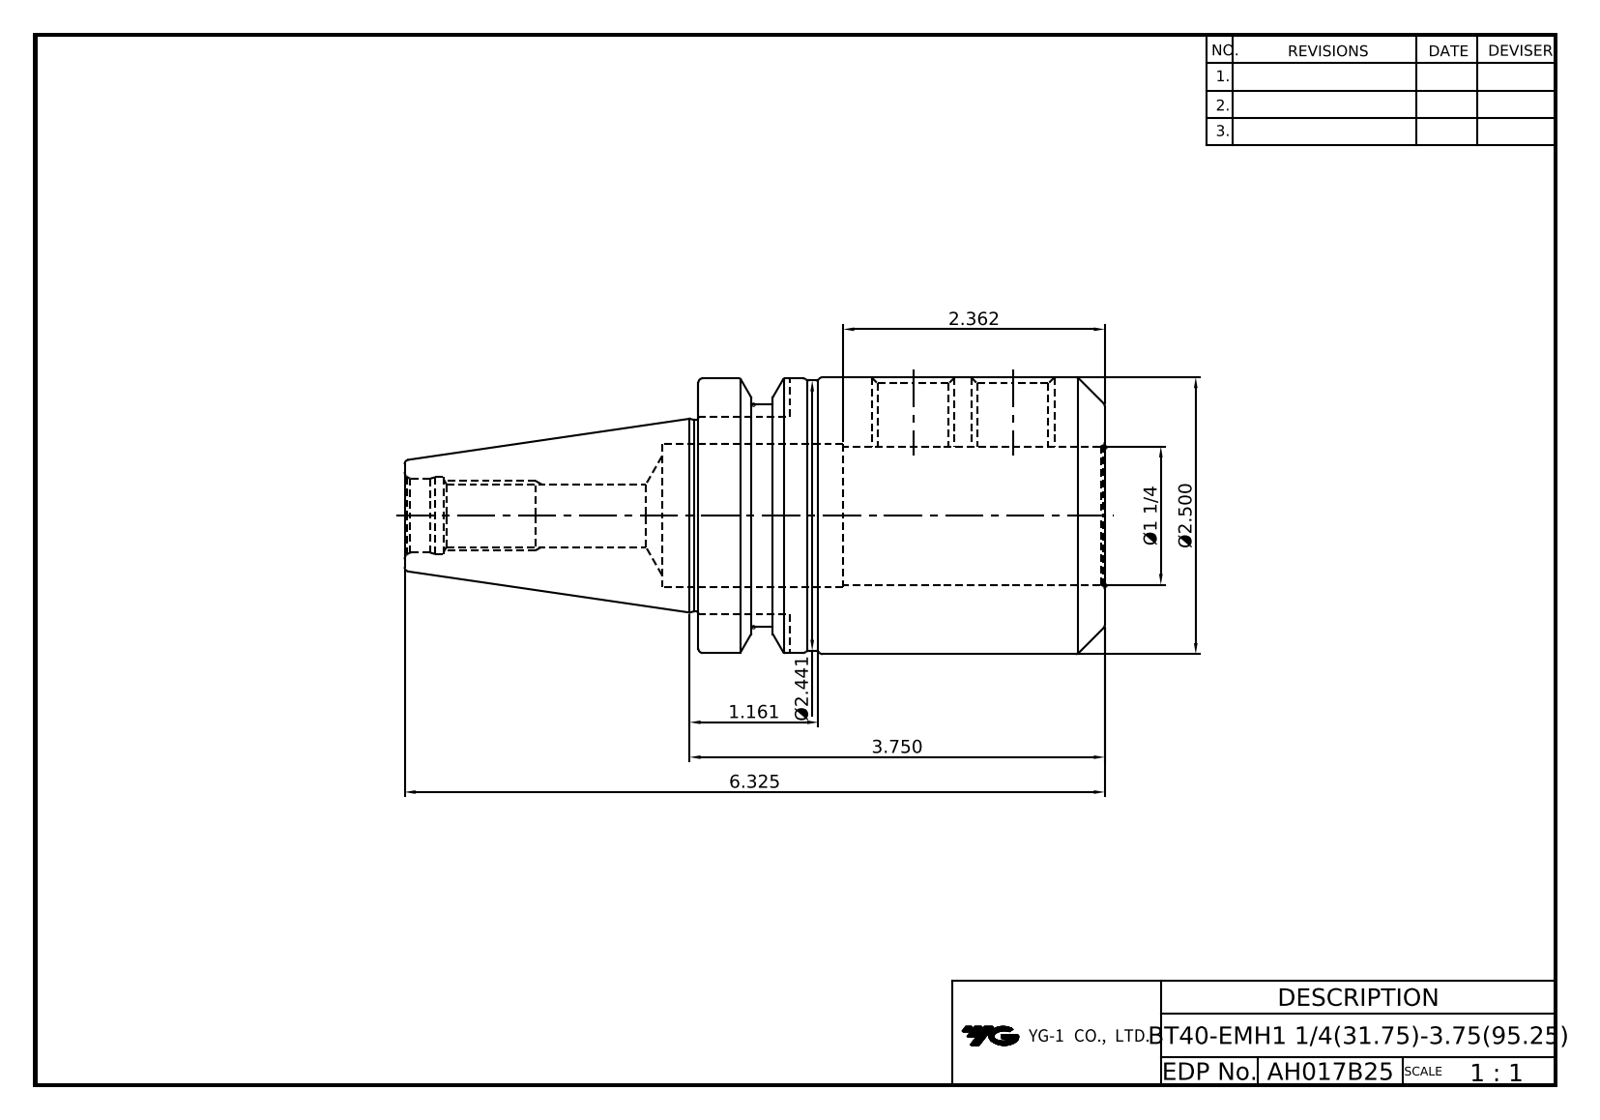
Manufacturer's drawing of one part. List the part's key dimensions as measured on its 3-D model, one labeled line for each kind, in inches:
Part name (STEP PRODUCT): LO-BT40-EMH31.75-95.25
STEP written by: Autodesk Inventor 2022 (AUTOMOTIVE_DESIGN)
Units: inches
Bodies: 1 solid, 55 faces (17 planar, 17 cylindrical, 21 other)
Overall size (bounding box): 6.325 × 2.5 × 2.5
Volume: 14.95 in³ · Surface area: 69.77 in²
Round holes (diameter × count): ⌀0.682 ×2, ⌀0.545 ×1, ⌀0.669 ×1, ⌀0.693 ×1, ⌀1.25 ×1, ⌀1.297 ×1
Round bosses / shafts (diameter × count): ⌀2.5 ×1, ⌀2.48 ×1, ⌀2.441 ×1, ⌀2.071 ×1, ⌀1.732 ×1
Partial cylindrical surfaces — rounded edges, fillets, slot ends (radius × count): R0.317 ×1
Main face-to-face distances: 3.671, 1.78, 0.329, 4, 0.634, 2.325, 2.654, 6.325, 3.327, 1.002
Hole centre spacings: 0.9
